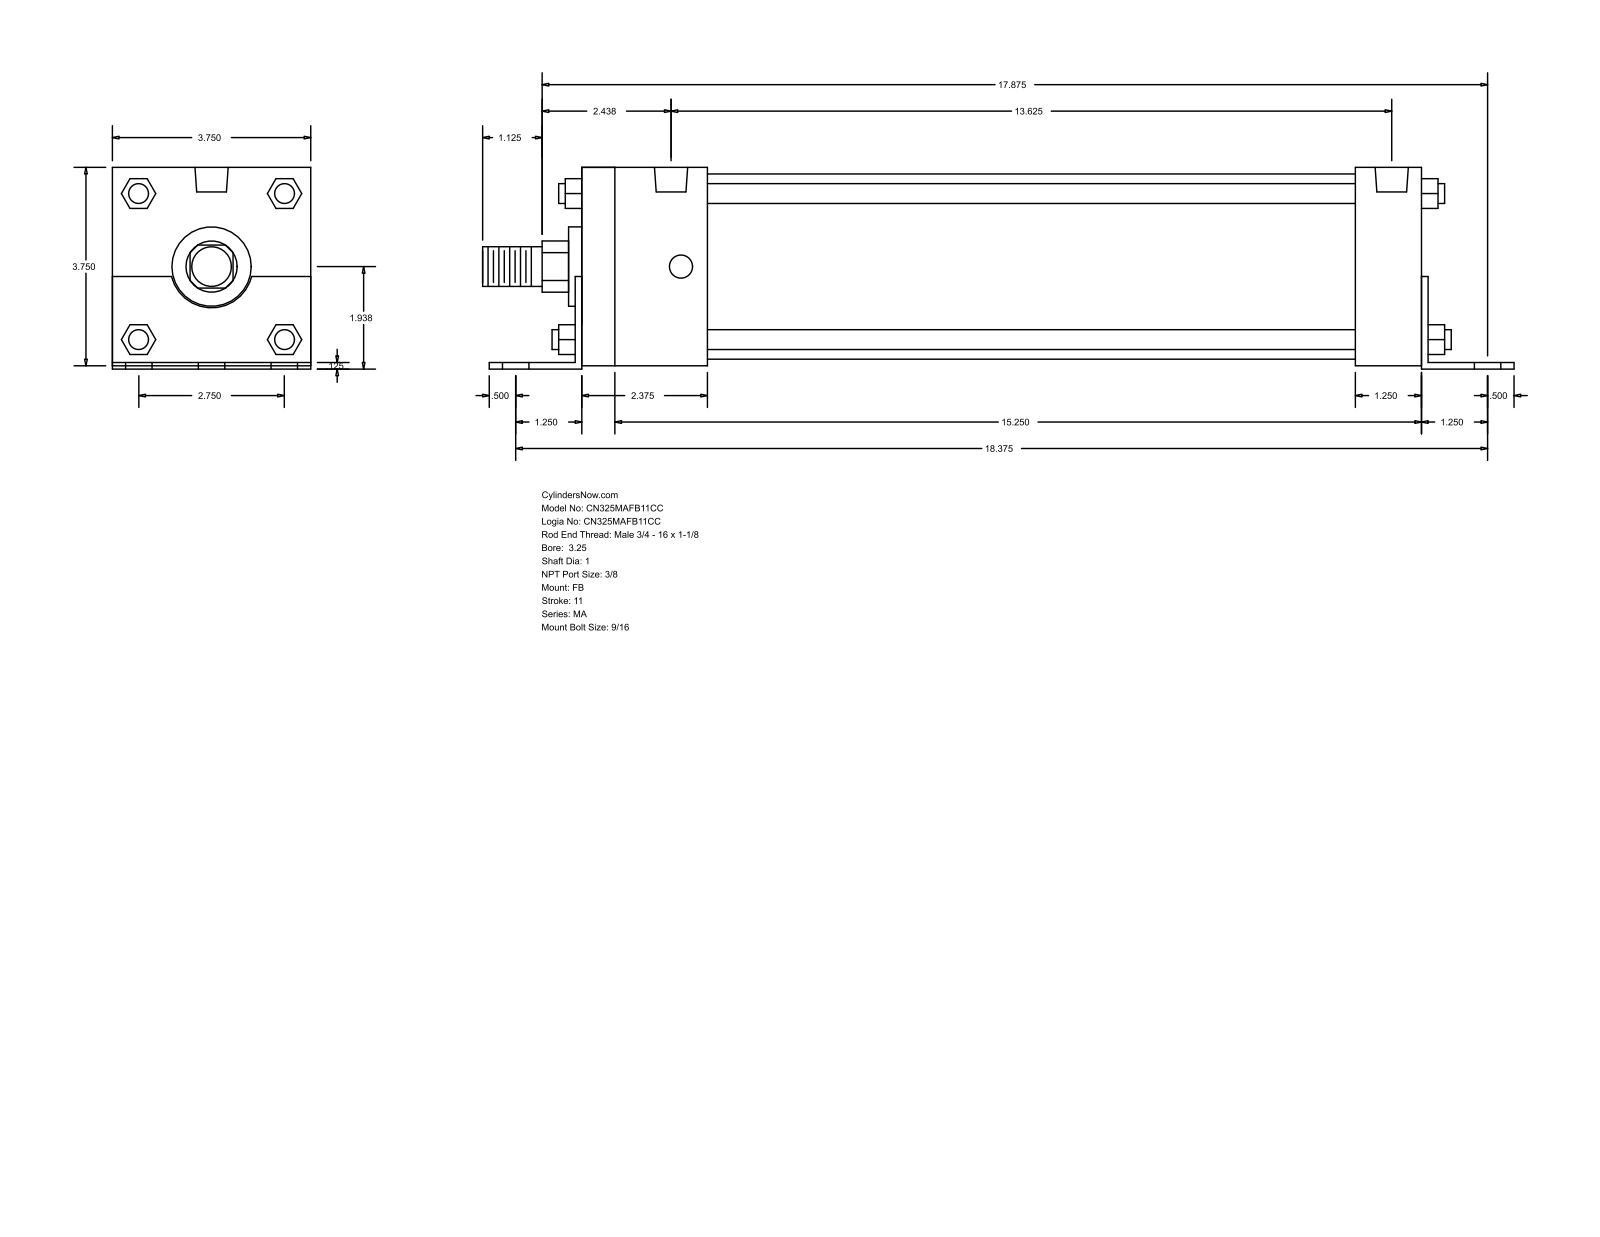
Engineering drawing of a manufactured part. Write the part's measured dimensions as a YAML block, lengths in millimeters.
part_name: "MA_FB__0325_1"
step_written_by: "GSSL Pune (CONFIG_CONTROL_DESIGN)"
units: millimeters
bodies: {solids: 0, faces: 140, planar: 105, cylindrical: 35, other: 0}
overall_size: [495.3, 96.84, 95.25]
round_holes:
  - {diameter: 14.29, count: 6}
  - {diameter: 11.11, count: 4}
  - {diameter: 15.93, count: 2}
round_bosses_or_shafts:
  - {diameter: 9.53, count: 4}
  - {diameter: 88.9, count: 1}
  - {diameter: 38.1, count: 1}
  - {diameter: 25.4, count: 1}
  - {diameter: 19.05, count: 1}
partial_cylinders:
  - {radius: 12.29, count: 1}
  - {radius: 19.81, count: 1}
face_to_face_distances: [95.24, 3.17, 1.59, 96.83, 1.58, 93.66, 3.18, 403.22, 409.57, 406.4]
hole_center_spacings: [34.92, 468.02, 466.72, 4.76, 57.78, 61.64, 69.84, 82.38]
